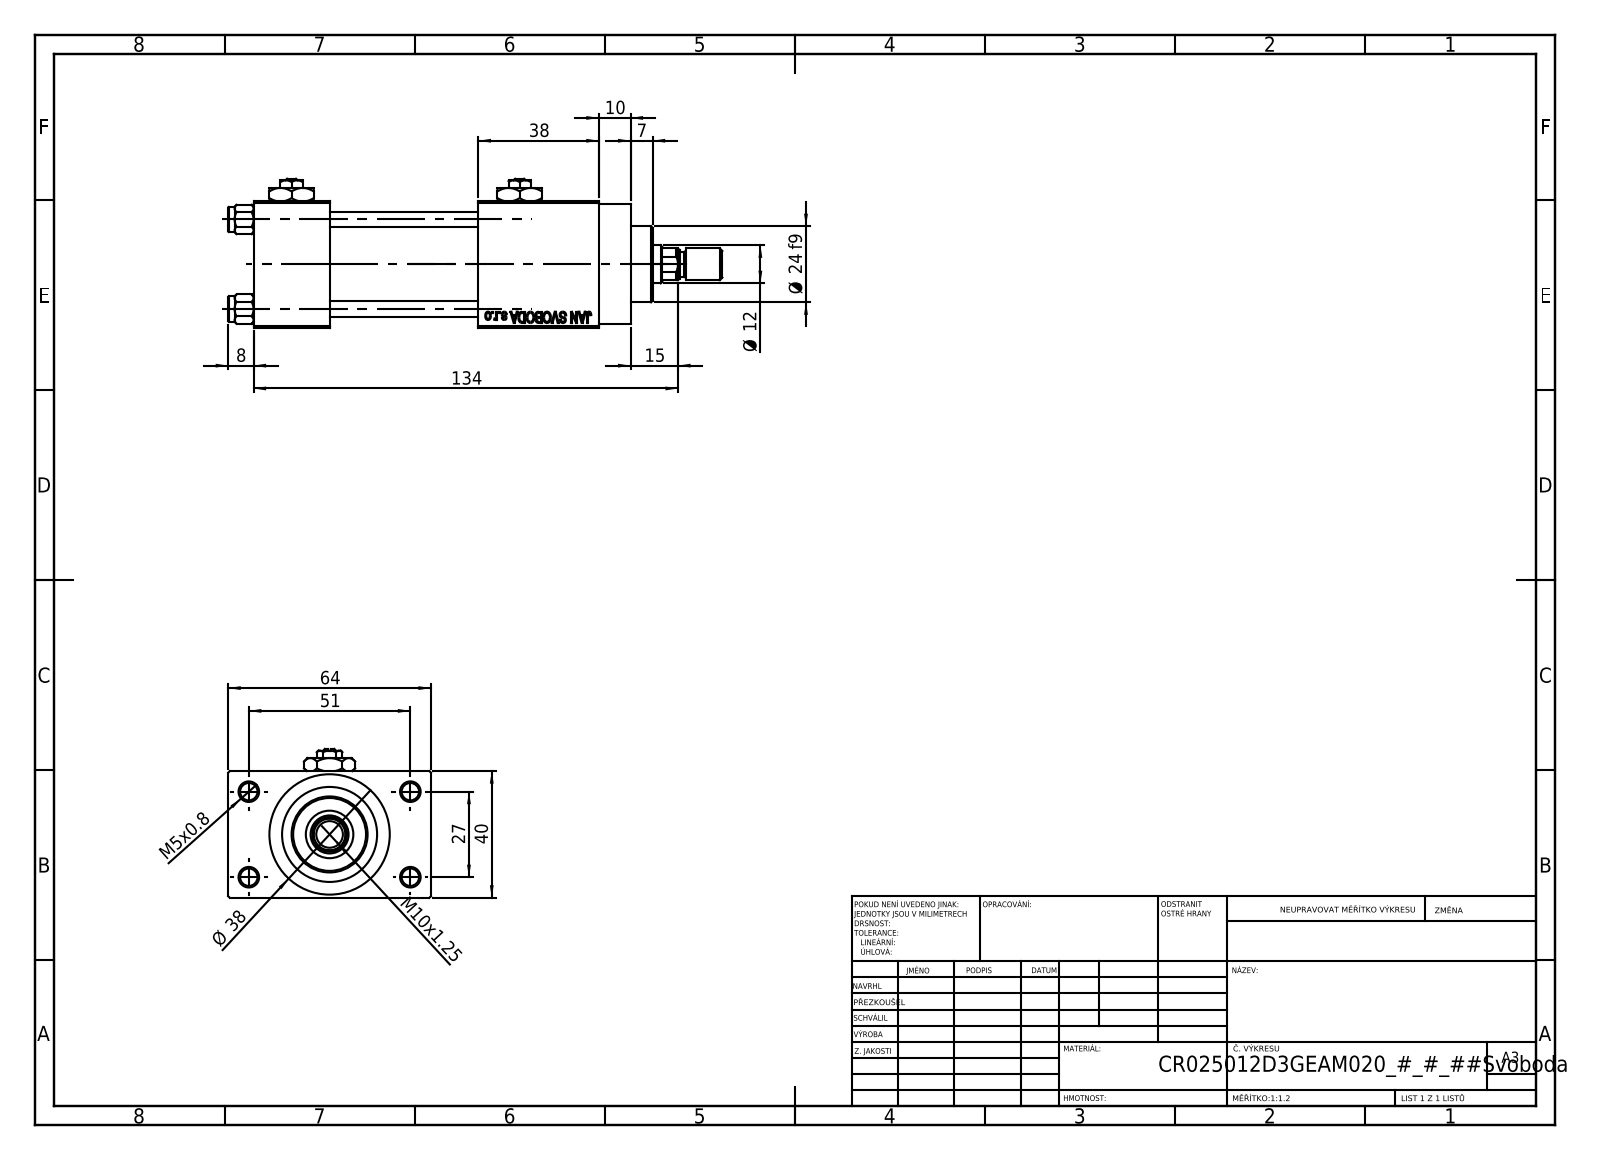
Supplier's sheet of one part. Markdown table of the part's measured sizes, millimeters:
| quantity | value |
| --- | --- |
| part name | ROD_END_AH; V215_VC_A; NUT_M5_D; V215CR_D_TYCINKA (+3 more) |
| STEP written by | SolidWorks 2019 (CONFIG_CONTROL_DESIGN) |
| units | millimeters |
| bodies | 14 solids, 1216 faces (546 planar, 104 cylindrical, 566 other) |
| overall size | 156 × 64 × 47 |
| volume | 175 245 mm³ |
| surface area | 63 925 mm² |
| round holes (diameter × count) | 5 × 4, 5.5 × 4, 20 × 3, 7 × 2, 13.16 × 2, 6.5 × 1, 12 × 1, 15 × 1, 25 × 1, 30 × 1 |
| round bosses / shafts (diameter × count) | 8 × 5, 38 × 1, 31 × 1, 24 × 1, 10 × 1 |
| partial cylindrical surfaces (radius × count) | 5.5 × 1 |
| main face-to-face distances | 40, 52, 12, 47, 71, 24, 64, 38, 85, 109 |
| hole center spacings | 11.37, 20.01, 28.3, 28.85, 29.89, 39.66, 48.34, 27 |
